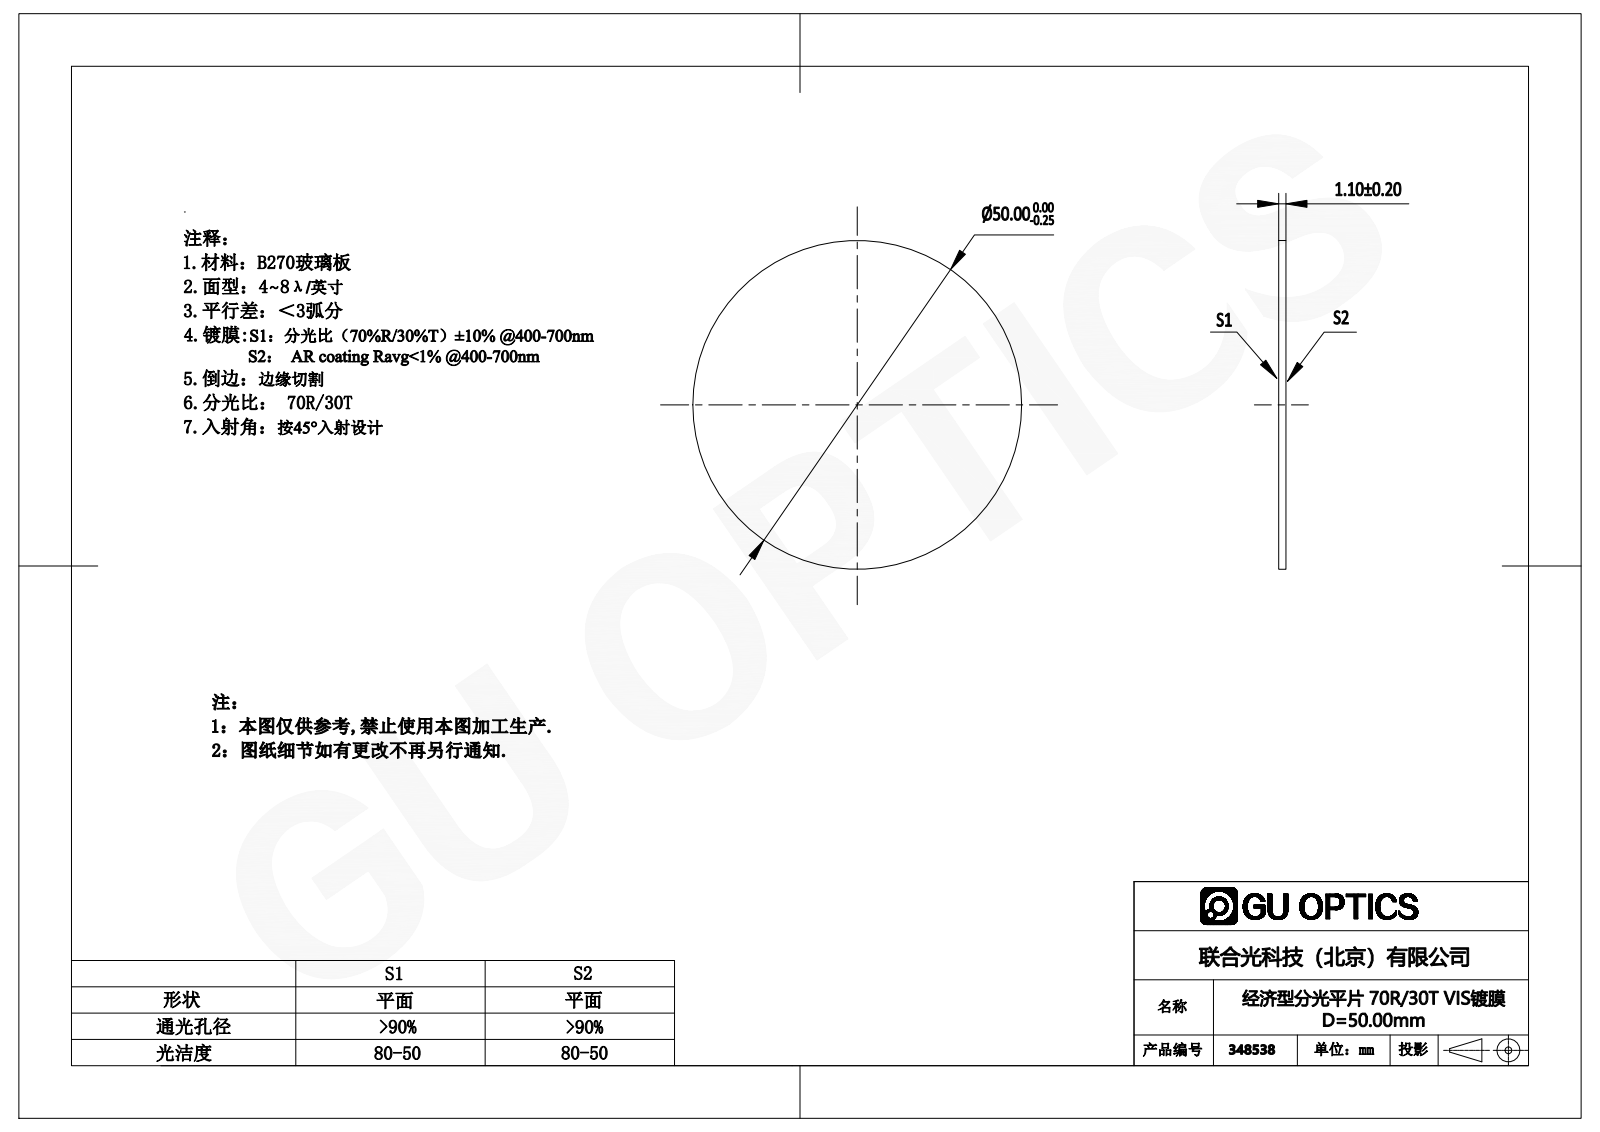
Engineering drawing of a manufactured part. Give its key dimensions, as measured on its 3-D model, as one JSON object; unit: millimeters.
{"part_name": "348510", "step_written_by": "SolidWorks 2016 (CONFIG_CONTROL_DESIGN)", "units": "millimeters", "bodies": {"solids": 1, "faces": 4, "planar": 2, "cylindrical": 2, "other": 0}, "overall_size": [50, 50, 1.1], "volume_mm3": 2160, "surface_area_mm2": 4100, "round_bosses_or_shafts": [[50, 1]], "face_to_face_distances": [1.1]}
